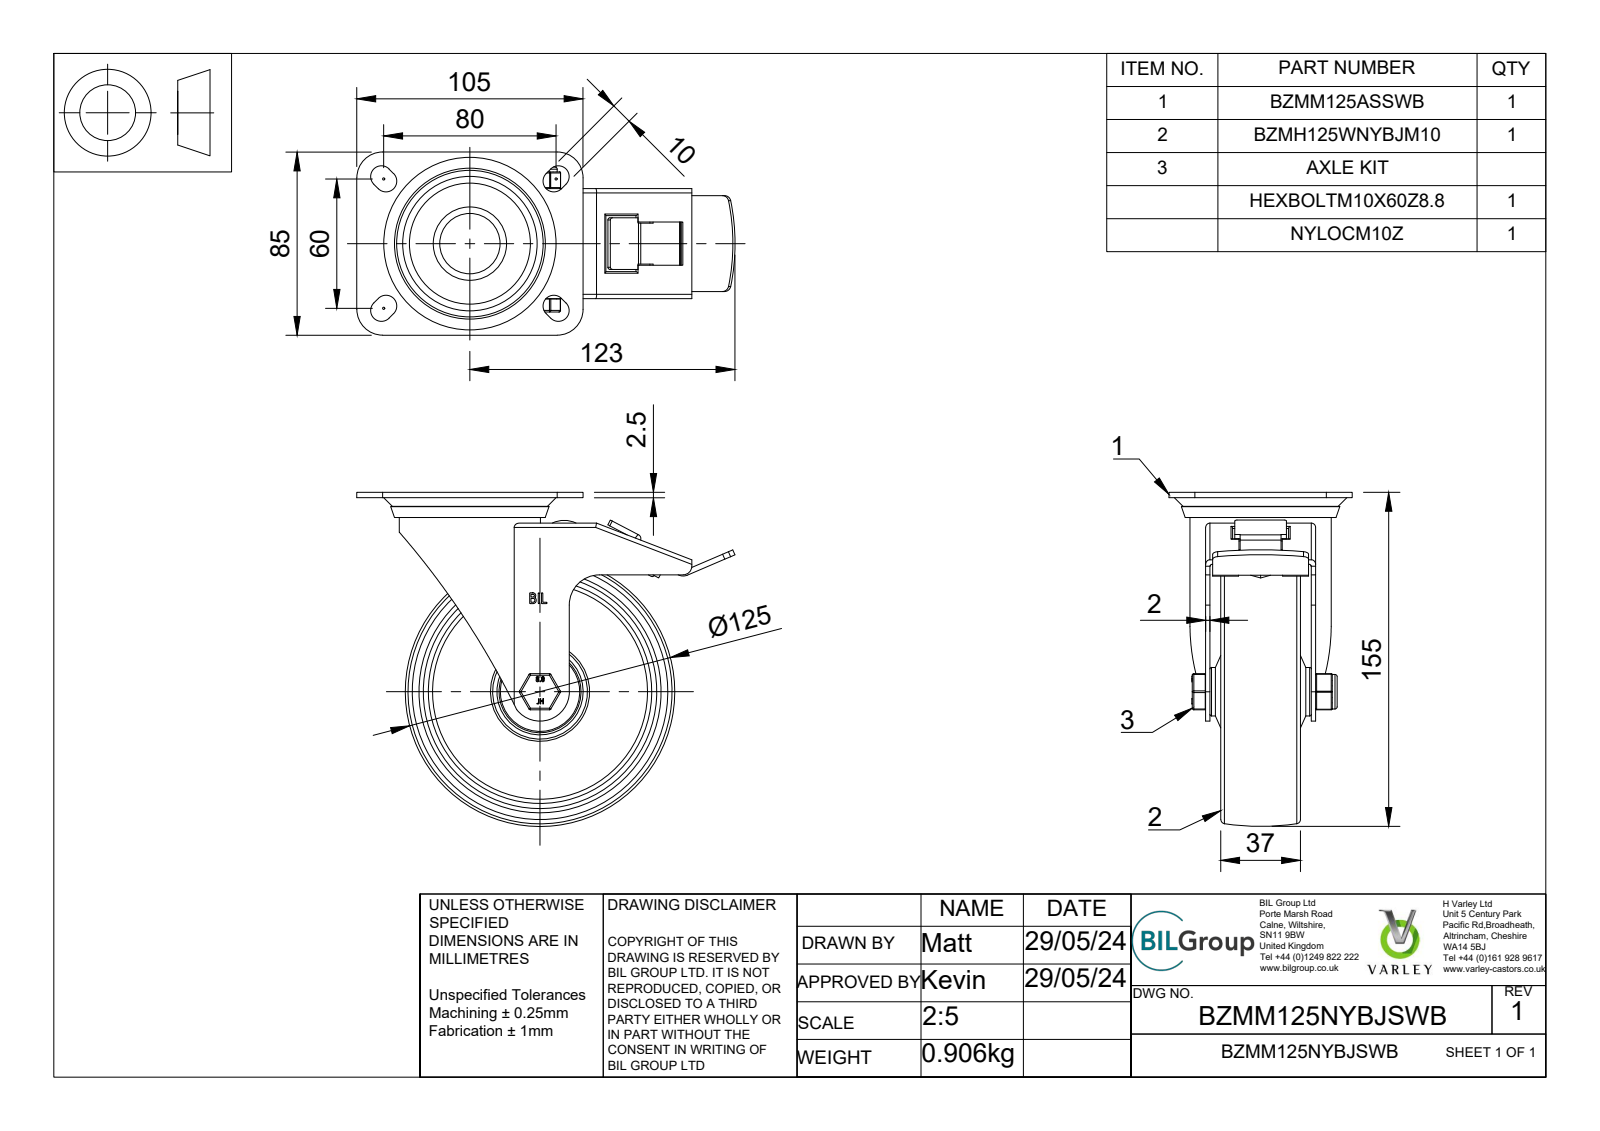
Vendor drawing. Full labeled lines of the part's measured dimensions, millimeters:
Part name (STEP PRODUCT): BZMM125NYBJSWB v4; BZMM125ASSWB - 47 v1; ZINC PLATED, PRESSED STEEL TOP PLATE; BEARING SEAL (+8 more)
STEP written by: Autodesk Translation Framework v13.14.0.145 (AUTOMOTIVE_DESIGN)
Units: millimetres
Bodies: 27 solids, 999 faces (463 planar, 254 cylindrical, 282 other)
Overall size (bounding box): 175.5 × 155 × 85
Volume: 299 557 mm³ · Surface area: 153 785 mm²
Round holes (diameter × count): ⌀6 ×2, ⌀40 ×2, ⌀10 ×1, ⌀10.2 ×1, ⌀12 ×1, ⌀15 ×1, ⌀20 ×1, ⌀22.5 ×1, ⌀25 ×1, ⌀28 ×1, ⌀30 ×1, ⌀31 ×1
Round bosses / shafts (diameter × count): ⌀65.5 ×1, ⌀44 ×1, ⌀38 ×1, ⌀34 ×1, ⌀30.5 ×1, ⌀28 ×1, ⌀23 ×1, ⌀19 ×1
Partial cylindrical surfaces — rounded edges, fillets, slot ends (radius × count): R0.5 ×18, R0.75 ×16, R1.5 ×12, R5 ×9, R1 ×7, R2 ×6, R12 ×5, R3 ×4
Main face-to-face distances: 2, 7, 22, 20, 29, 5, 27, 49, 9, 2.5
Hole centre spacings: 43.75
